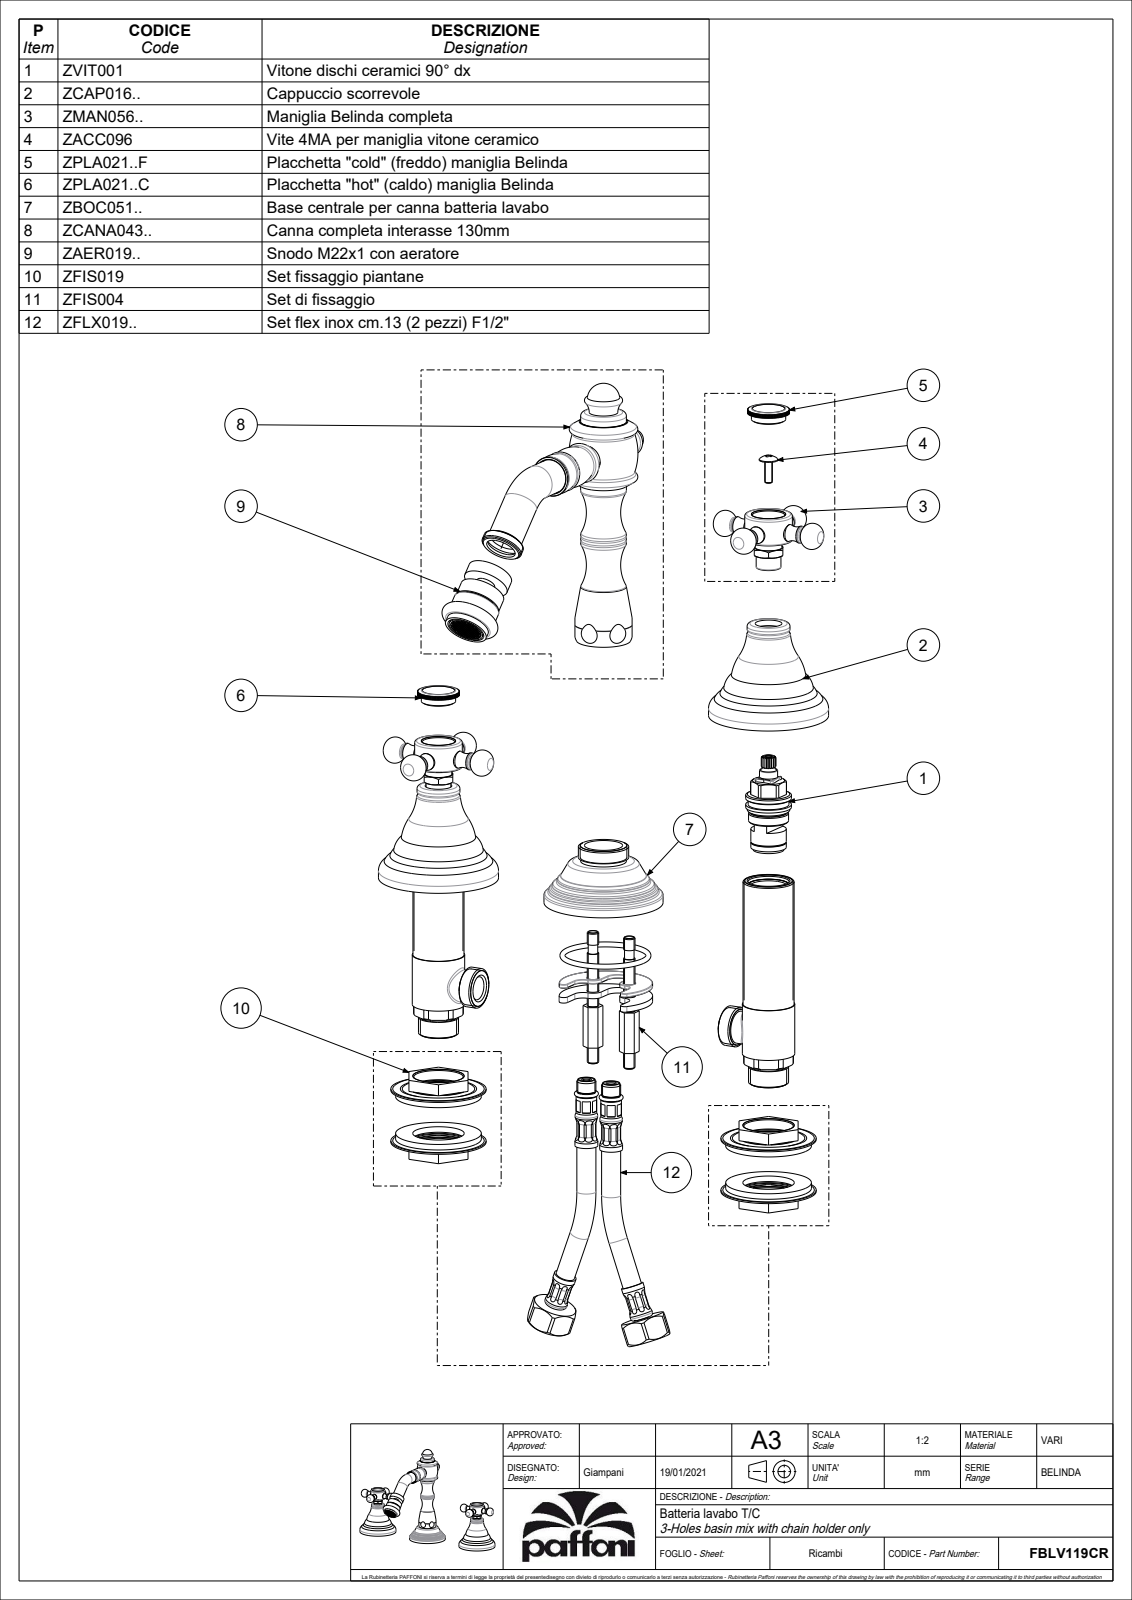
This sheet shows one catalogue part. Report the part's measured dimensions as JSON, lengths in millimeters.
{"part_name": "FBLV119CR", "step_written_by": "CREO PARAMETRIC BY PTC INC, 2020044 (CONFIG_CONTROL_DESIGN)", "units": "millimeters", "bodies": {"solids": 3, "faces": 1110, "planar": 464, "cylindrical": 326, "other": 320}, "overall_size": [264.07, 204.4, 174.66], "volume_mm3": 335714, "surface_area_mm2": 73367, "round_holes": [[5, 2], [9, 2], [10, 2], [11, 2], [20, 1], [24.1, 1], [48.5, 1]], "round_bosses_or_shafts": [[25, 3], [9, 3], [7, 3], [63, 2], [24, 2], [22.5, 2], [18, 2], [14, 2]], "partial_cylinders_radius": [[11, 2]], "face_to_face_distances": [30, 60.4, 5, 2, 58.4, 28.4, 32, 18, 29.2, 24.2], "hole_center_spacings": [9.01, 13.46, 13.6, 22.61, 15, 22]}
